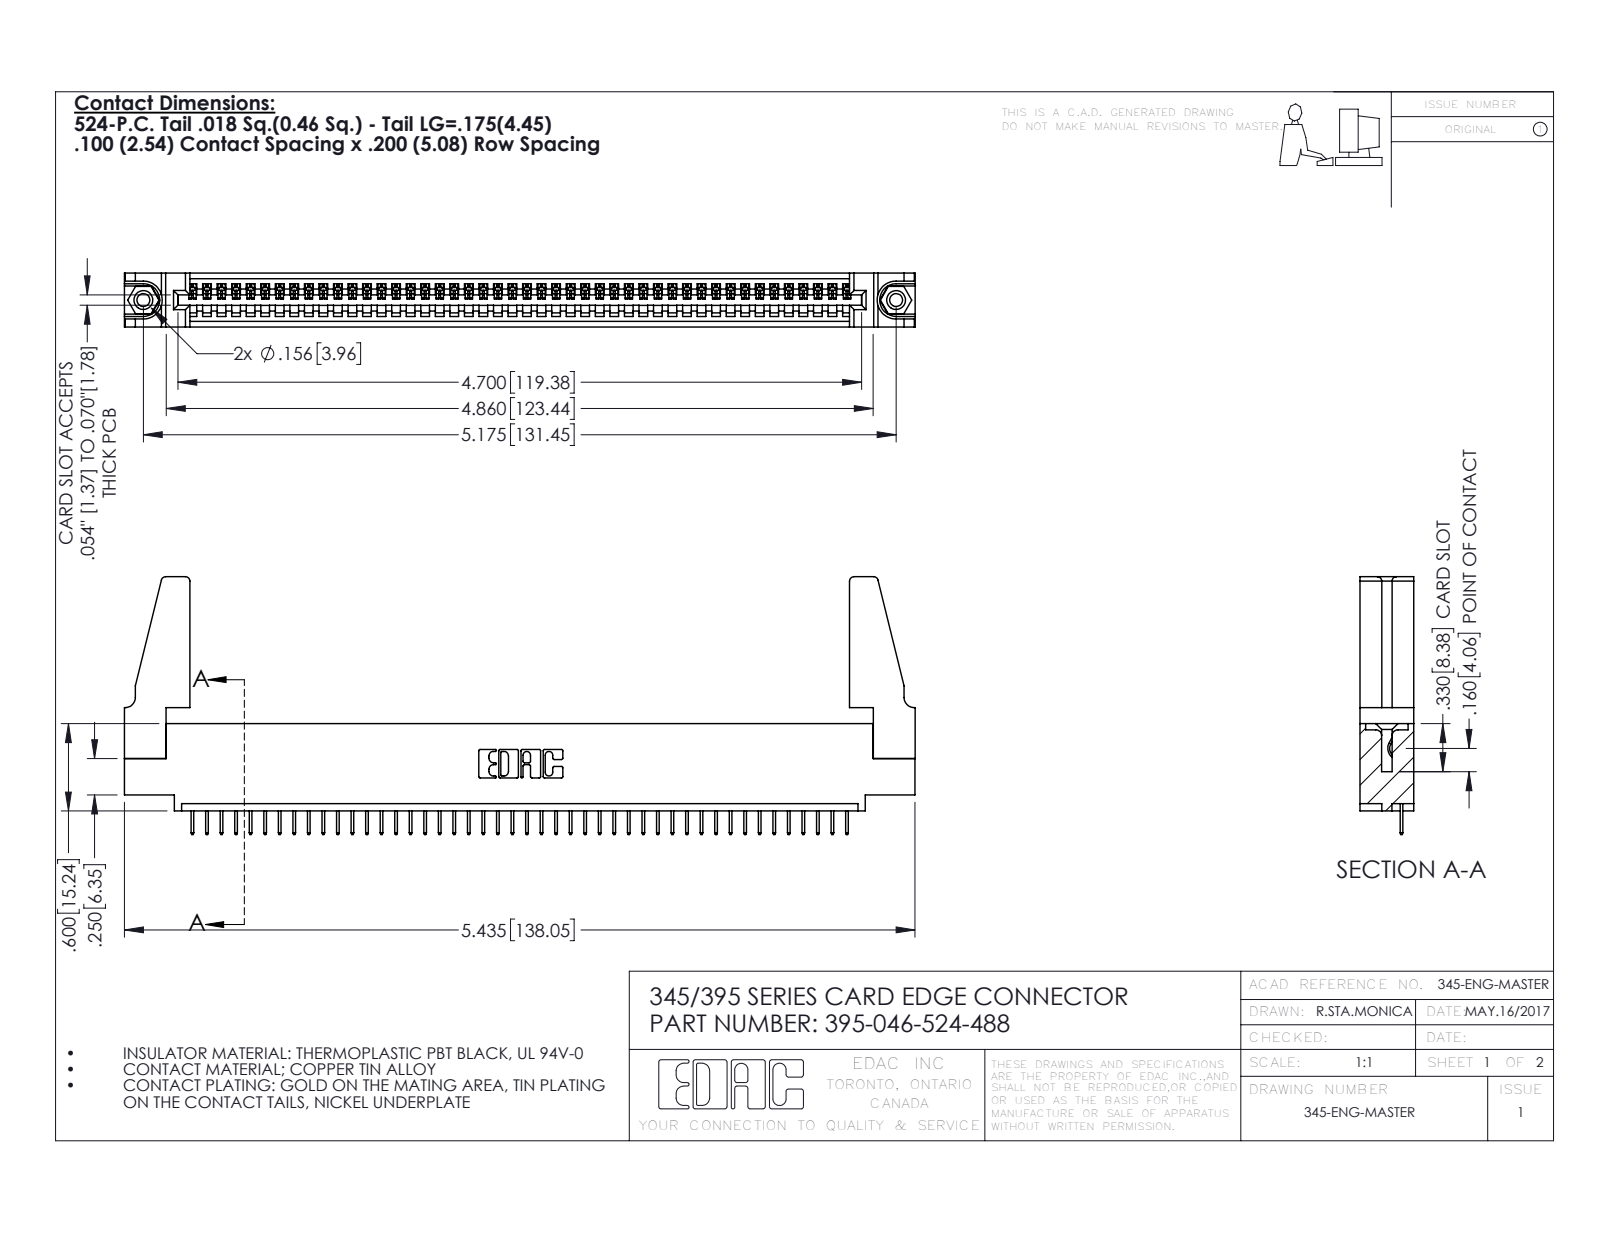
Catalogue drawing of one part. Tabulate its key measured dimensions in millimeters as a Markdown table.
| quantity | value |
| --- | --- |
| part name | 395-046-524-488; 345-250-001_345-250-001-102; 345-220-078_345-220-088; 345 Part_0.110 Offset - 0.156 Dia-TH (+1 more) |
| STEP written by | SolidWorks 2016 (CONFIG_CONTROL_DESIGN) |
| units | millimeters |
| bodies | 51 solids, 3106 faces (2272 planar, 818 cylindrical, 16 other) |
| overall size | 138.1 × 45 × 9.4 |
| volume | 16 100 mm³ |
| surface area | 19 820 mm² |
| round holes (diameter × count) | 2.3 × 2, 3.2 × 2, 4 × 2, 1.6 × 1 |
| round bosses / shafts (diameter × count) | 3.9 × 2 |
| partial cylindrical surfaces (radius × count) | 0.2 × 92, 0.3 × 22, 0.8 × 8, 0.2 × 6, 0.8 × 6, 0.7 × 3, 0.8 × 2, 1 × 2 |
| main face-to-face distances | 1.8, 9.4, 7.6, 5.1, 2.5, 6.9, 0.6, 5.7, 1.8, 3.8 |
| hole center spacings | 6.9, 125.5, 131.4 |
